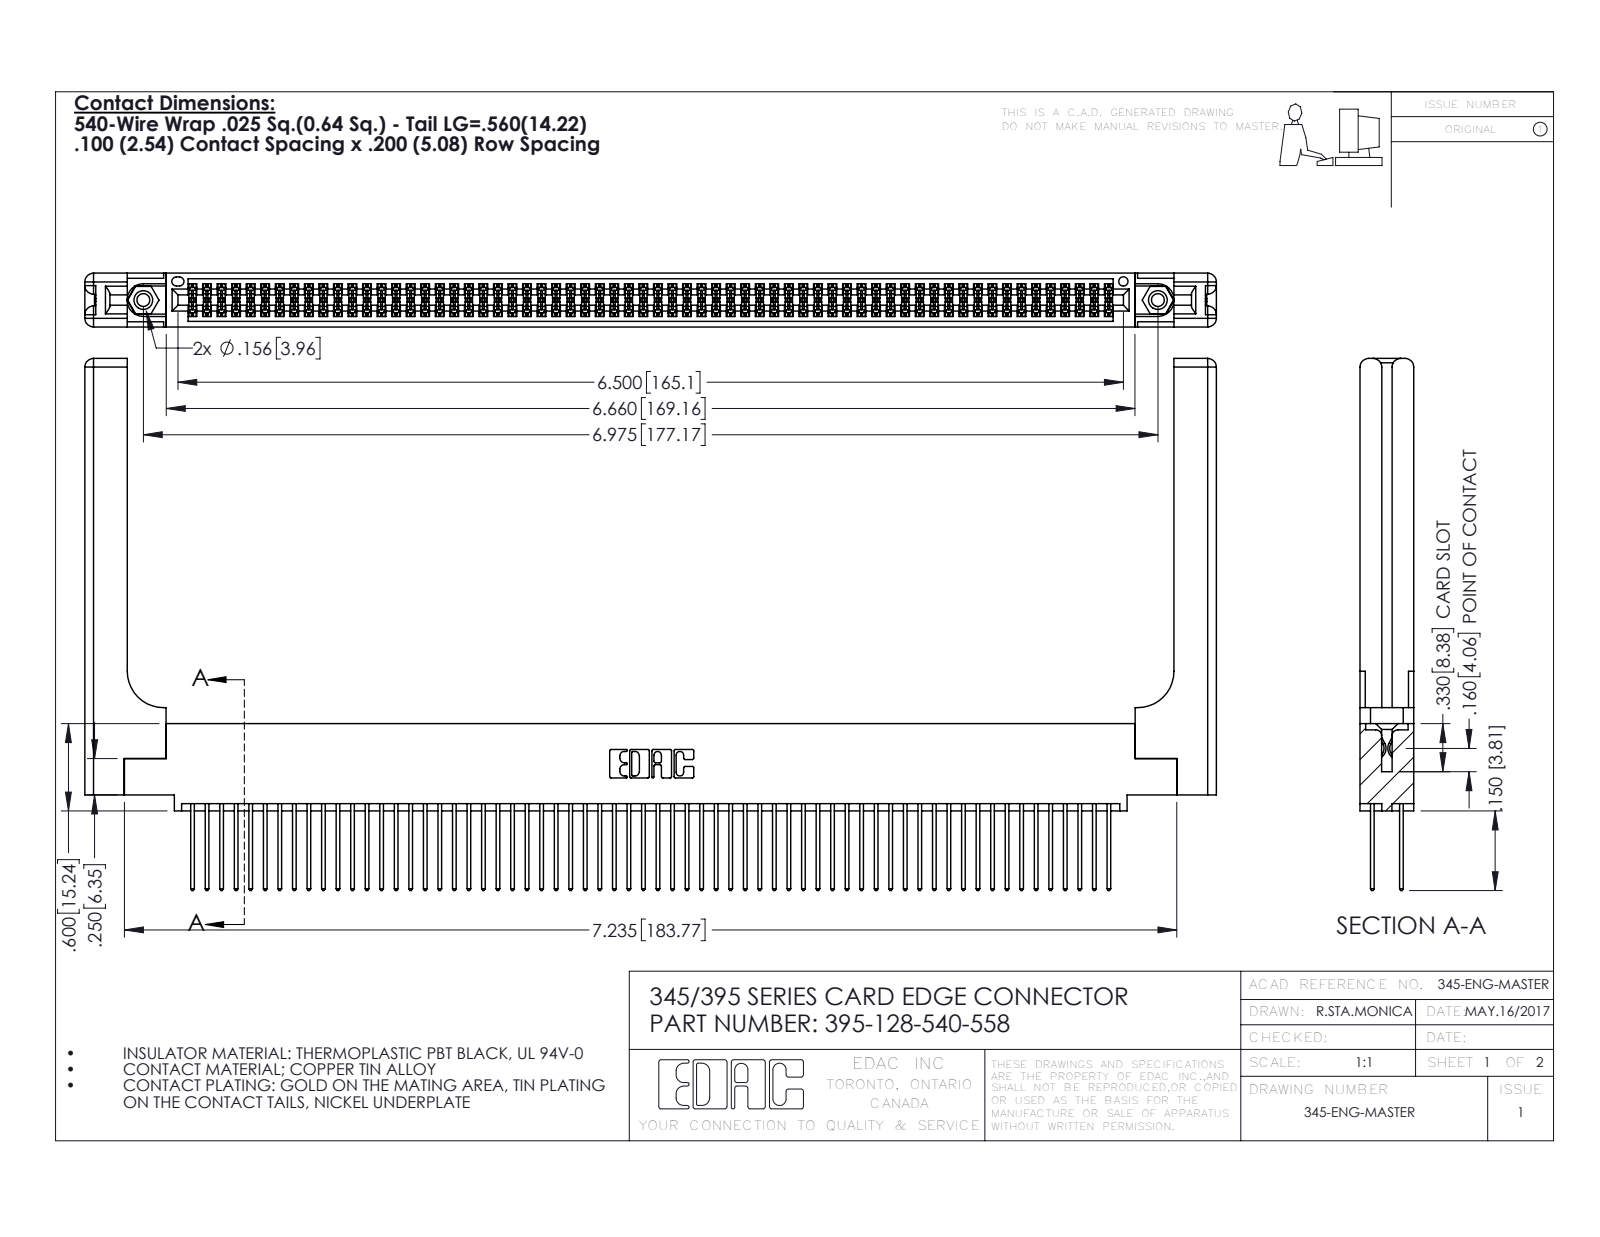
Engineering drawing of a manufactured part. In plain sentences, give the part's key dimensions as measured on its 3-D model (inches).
The part is named "345-250-001_345-250-001-102; 345-292-001_345-293-140; 345 Part_0.110 Offset - 0.156 Dia-TH; 345-220-058_345-220-058 (+1 more)". Its 3-D file was written by "SolidWorks 2016 (CONFIG_CONTROL_DESIGN)". It is 133 solids with 6786 faces: 4456 planar, 2270 cylindrical and 60 other. Overall it measures 7.779 by 3.657 by 0.37 inches. Its volume is 1.726 cubic inches and its surface area 57.52 square inches. Round holes: 2 of diameter 0.089, 2 of diameter 0.125, 2 of diameter 0.156, 1 of diameter 0.064. Round bosses or shafts: 2 of diameter 0.155. Partial cylindrical surfaces (rounded edges, fillets, slot ends): 192 of radius 0.006, 128 of radius 0.01, 22 of radius 0.01, 16 of radius 0.06, 6 of radius 0.007, 6 of radius 0.031, 3 of radius 0.026, 2 of radius 0.014. The main face-to-face distances are 0.072, 0.298, 0.37, 0.098, 0.272, 0.025, 0.2, 0.225, 0.175, 0.148. The hole center spacings are 0.27, 6.739, 6.975.
